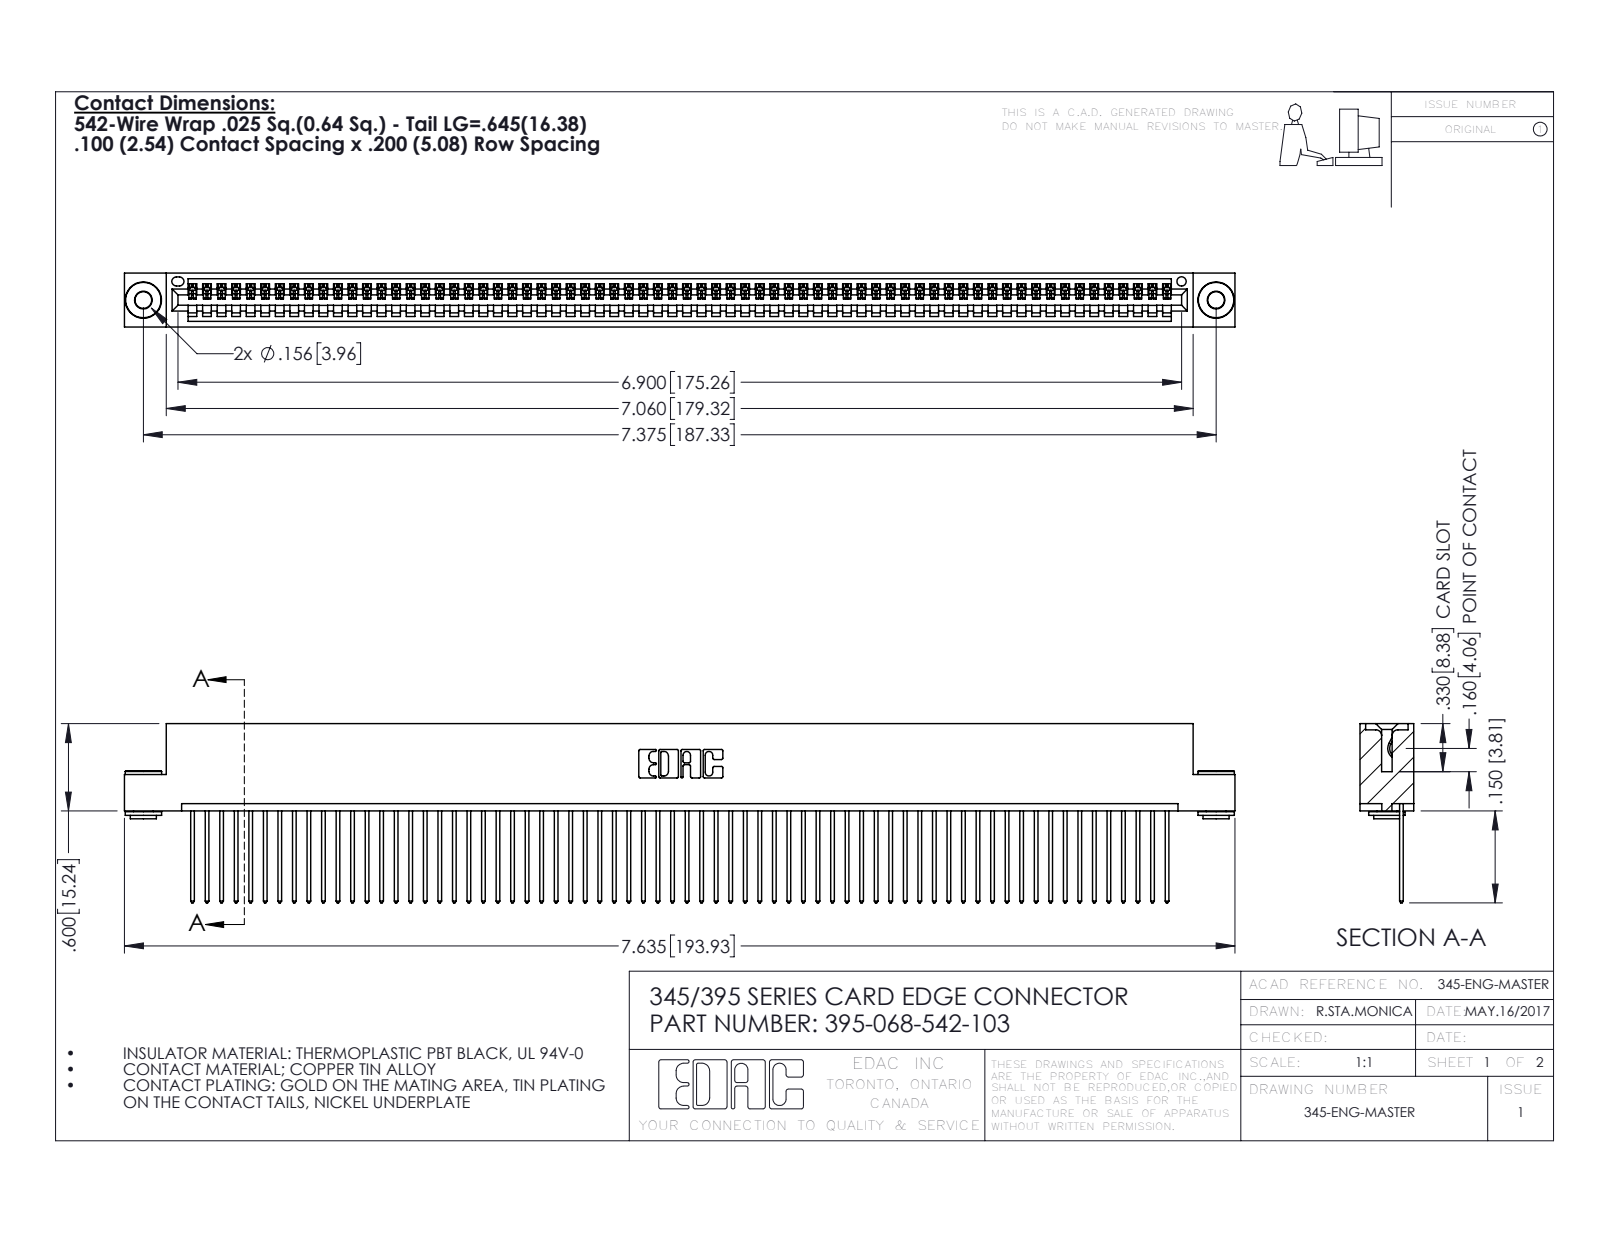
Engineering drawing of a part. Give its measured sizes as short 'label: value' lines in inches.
name: 345 Part_Flush Mounting Lugs - 0.156 Dia-TH; 395-068-542-103; 345-250-002_345-250-002-102; 345-292-001_345-293-142
written by: SolidWorks 2016 (CONFIG_CONTROL_DESIGN)
unit: in
bodies: 71 solids, 4108 faces (2810 planar, 1290 cylindrical, 8 other)
size: 7.635 × 1.232 × 0.37
volume: 1.147 in³; area: 41.09 in²
holes: 2× ⌀0.116, 2× ⌀0.156, 1× ⌀0.064
bosses: 2× ⌀0.25, 2× ⌀0.18, 2× ⌀0.136
rounds: 136× R0.006, 136× R0.01, 22× R0.01, 6× R0.007, 6× R0.031, 3× R0.026, 2× R0.031, 2× R0.04
face distances: 0.072, 0.298, 0.025, 0.098, 0.272, 0.37, 0.2, 0.225, 0.149, 0.072
hole spacings: 0.27, 7.139, 7.375
